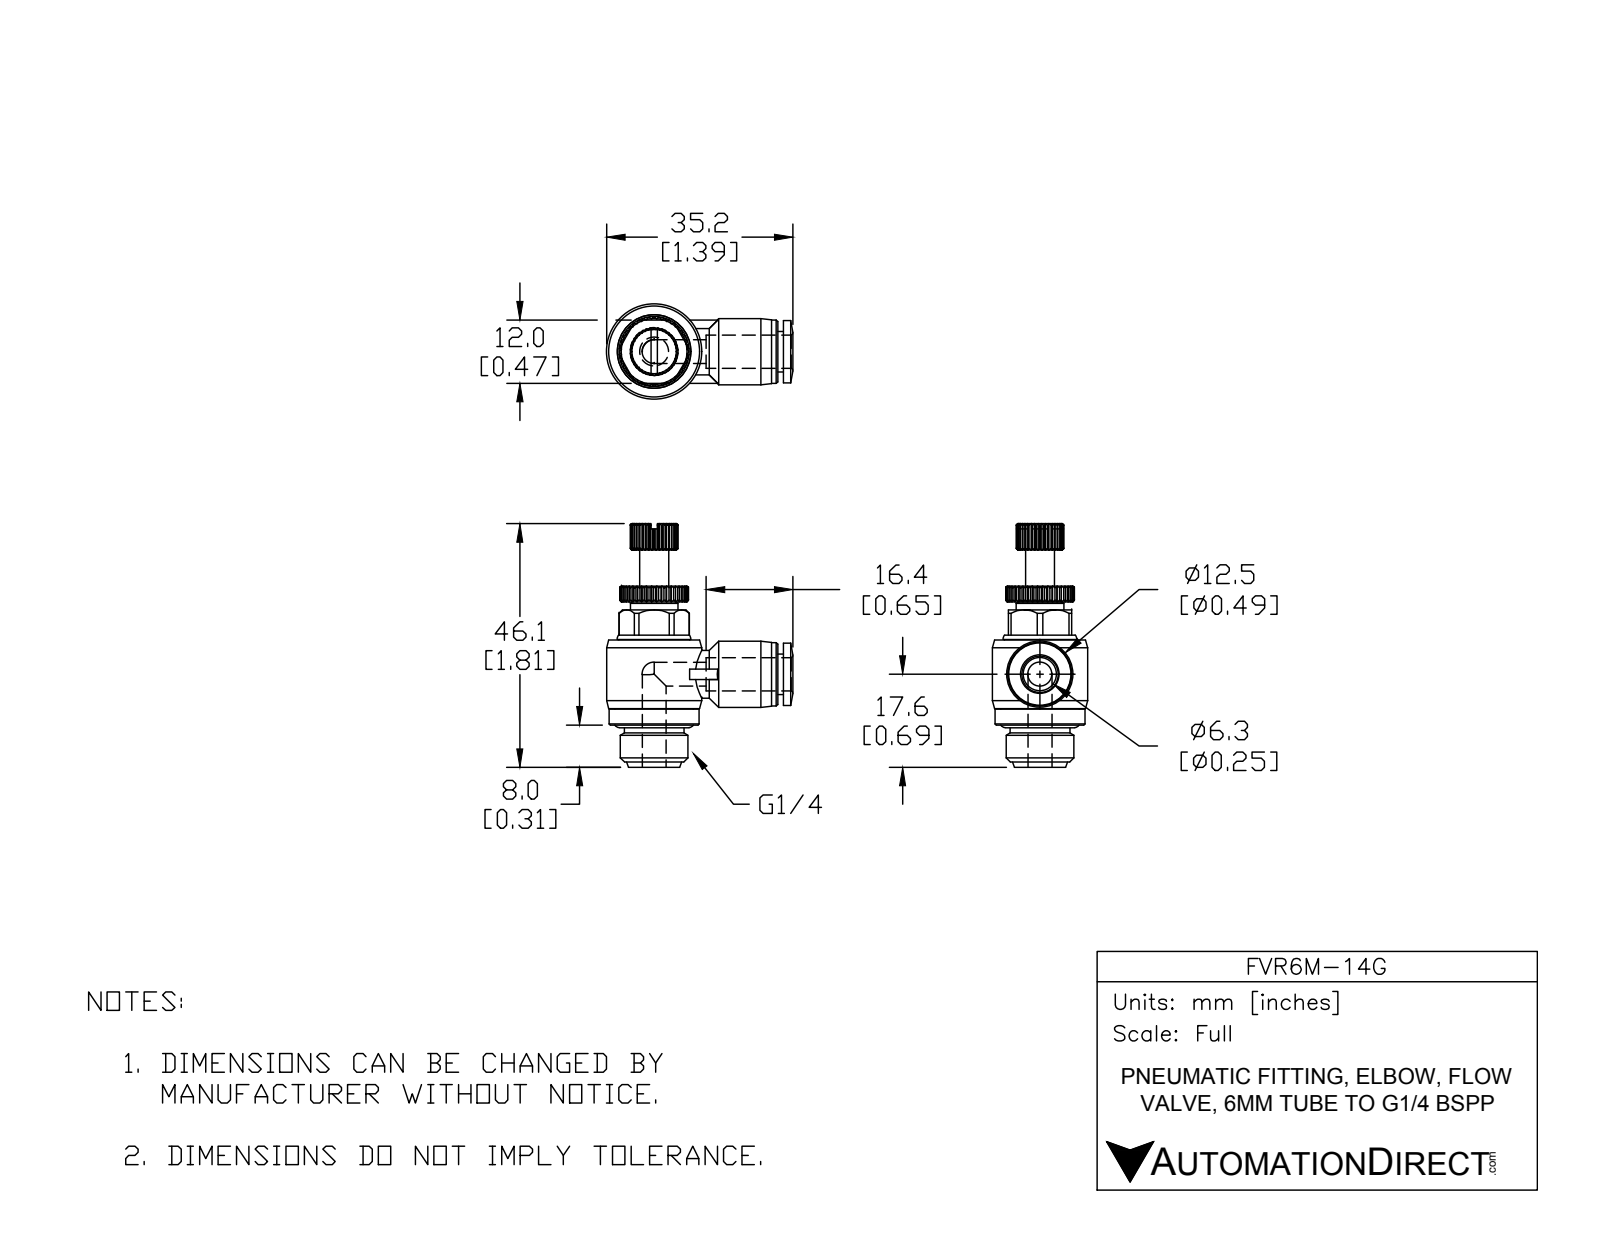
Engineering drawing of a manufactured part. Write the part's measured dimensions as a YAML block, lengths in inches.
part_name: "FVR6M-14G"
step_written_by: "SolidWorks 2015 (AUTOMOTIVE_DESIGN)"
units: inches
bodies: {solids: 2, faces: 516, planar: 196, cylindrical: 118, other: 202}
overall_size: [1.815, 1.388, 0.709]
volume: 0.457
surface_area: 7.077
round_holes:
  - {diameter: 0.177, count: 2}
  - {diameter: 0.248, count: 1}
round_bosses_or_shafts:
  - {diameter: 0.354, count: 2}
  - {diameter: 0.709, count: 1}
  - {diameter: 0.669, count: 1}
  - {diameter: 0.583, count: 1}
  - {diameter: 0.528, count: 1}
  - {diameter: 0.504, count: 1}
  - {diameter: 0.492, count: 1}
  - {diameter: 0.472, count: 1}
partial_cylinders:
  - {radius: 0.256, count: 1}
  - {radius: 0.262, count: 1}
face_to_face_distances: [0.402, 0.472, 0.118, 0.283, 0.234, 0.917, 0.913, 0.516, 0.512, 0.795]
